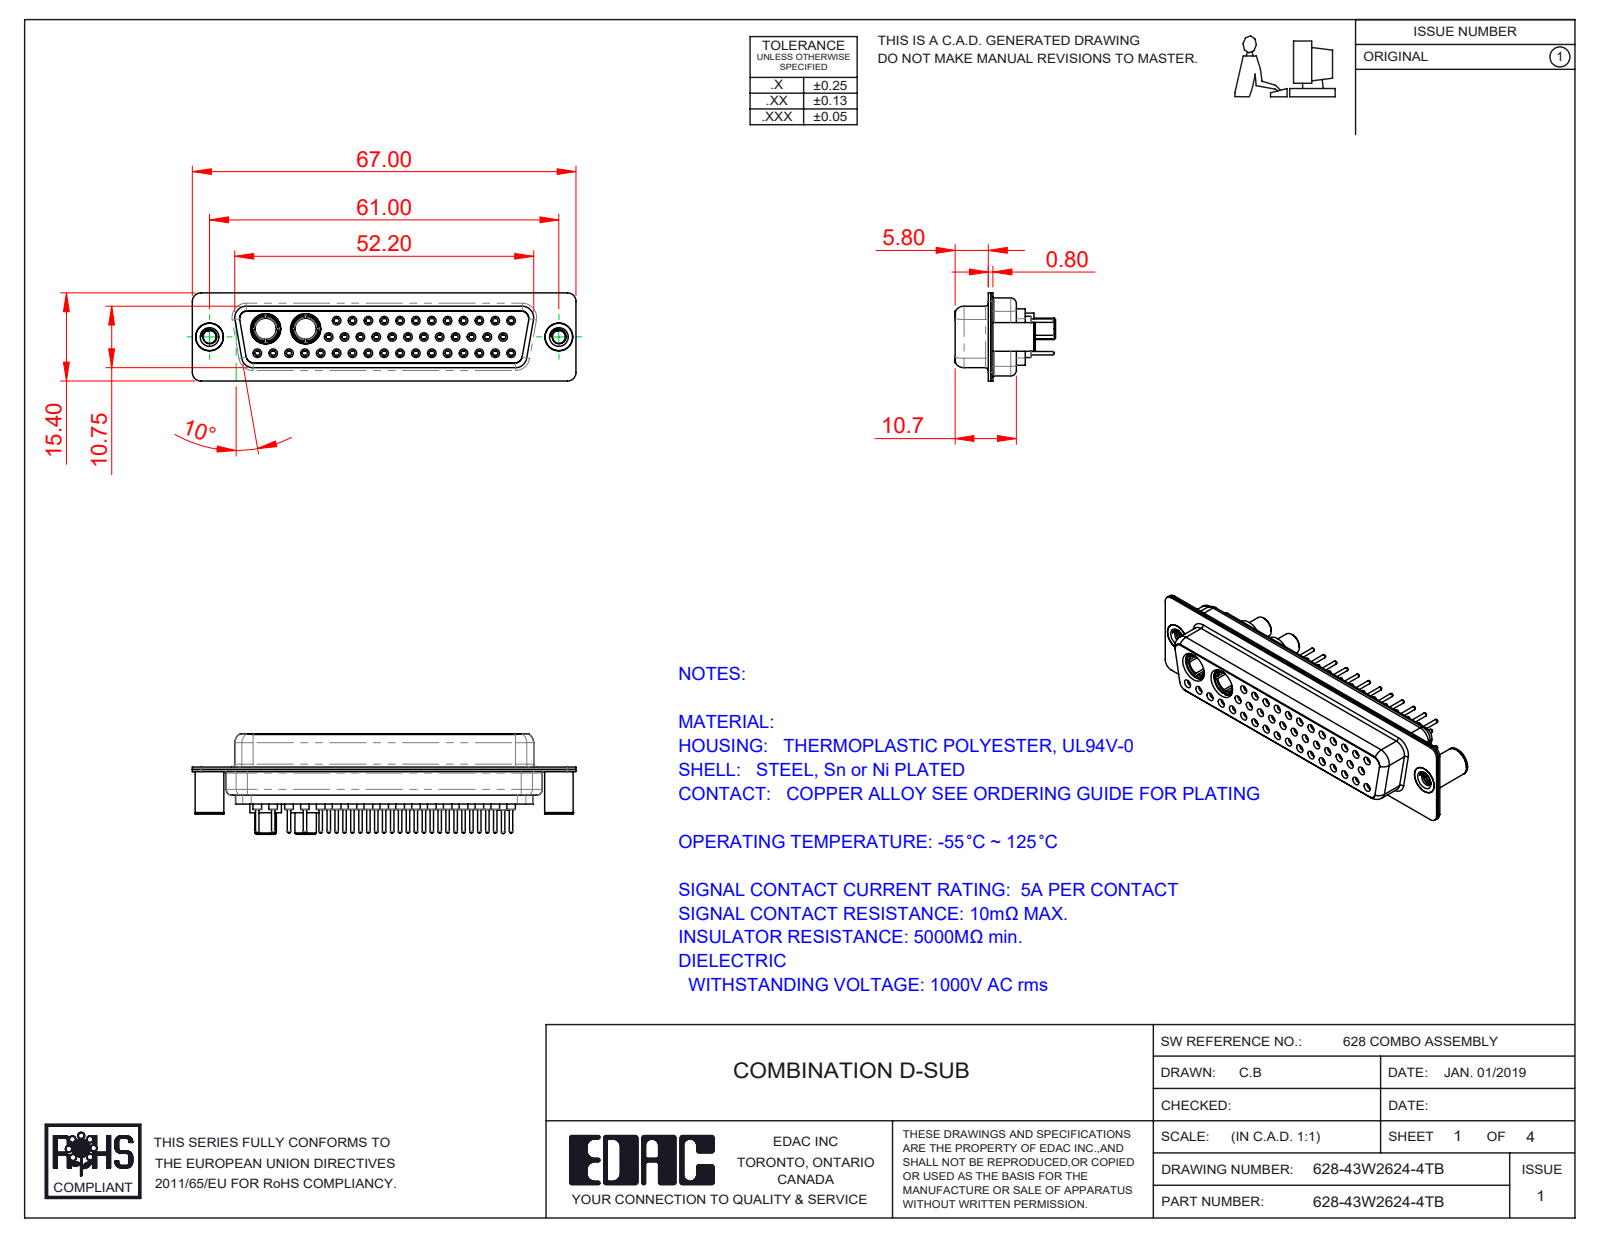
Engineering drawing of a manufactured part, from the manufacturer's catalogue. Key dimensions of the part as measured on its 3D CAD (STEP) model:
Part name (STEP PRODUCT): 628Combo Contact Row 3_24; 628-43W2624-4TB; 628Combo Contact Row 2_24; 628Combo Threaded Board Spacer_B (+5 more)
STEP written by: SolidWorks 2016 (CONFIG_CONTROL_DESIGN)
Units: millimetres
Bodies: 50 solids, 2726 faces (740 planar, 994 cylindrical, 992 other)
Overall size (bounding box): 67 × 17.55 × 15.4
Volume: 7 175 mm³ · Surface area: 14 878 mm²
Round holes (diameter × count): ⌀0.9 ×41, ⌀1.1 ×41, ⌀1.5 ×41, ⌀2 ×41, ⌀1.6 ×29, ⌀1.7 ×12, ⌀4.85 ×4, ⌀2.26 ×2, ⌀3.26 ×2, ⌀3.7 ×2, ⌀4 ×2, ⌀4.05 ×2
Round bosses / shafts (diameter × count): ⌀2.2 ×41, ⌀0.6 ×41, ⌀1.6 ×12, ⌀5.5 ×2, ⌀5.2 ×2, ⌀5 ×2, ⌀4.96 ×2, ⌀4.95 ×2
Partial cylindrical surfaces — rounded edges, fillets, slot ends (radius × count): R1.5 ×16, R1.35 ×12, R2 ×12, R1.6 ×8, R0.25 ×4, R0.5 ×4, R0.6 ×4, R0.65 ×4
Main face-to-face distances: 0.4, 6.45, 11.33, 6.05, 1.87, 10.35, 10.93, 12.25, 6.2, 5.8
Hole centre spacings: 2.77, 3.16, 5.54, 8.31, 11.08, 13.85, 16.62, 19.39
